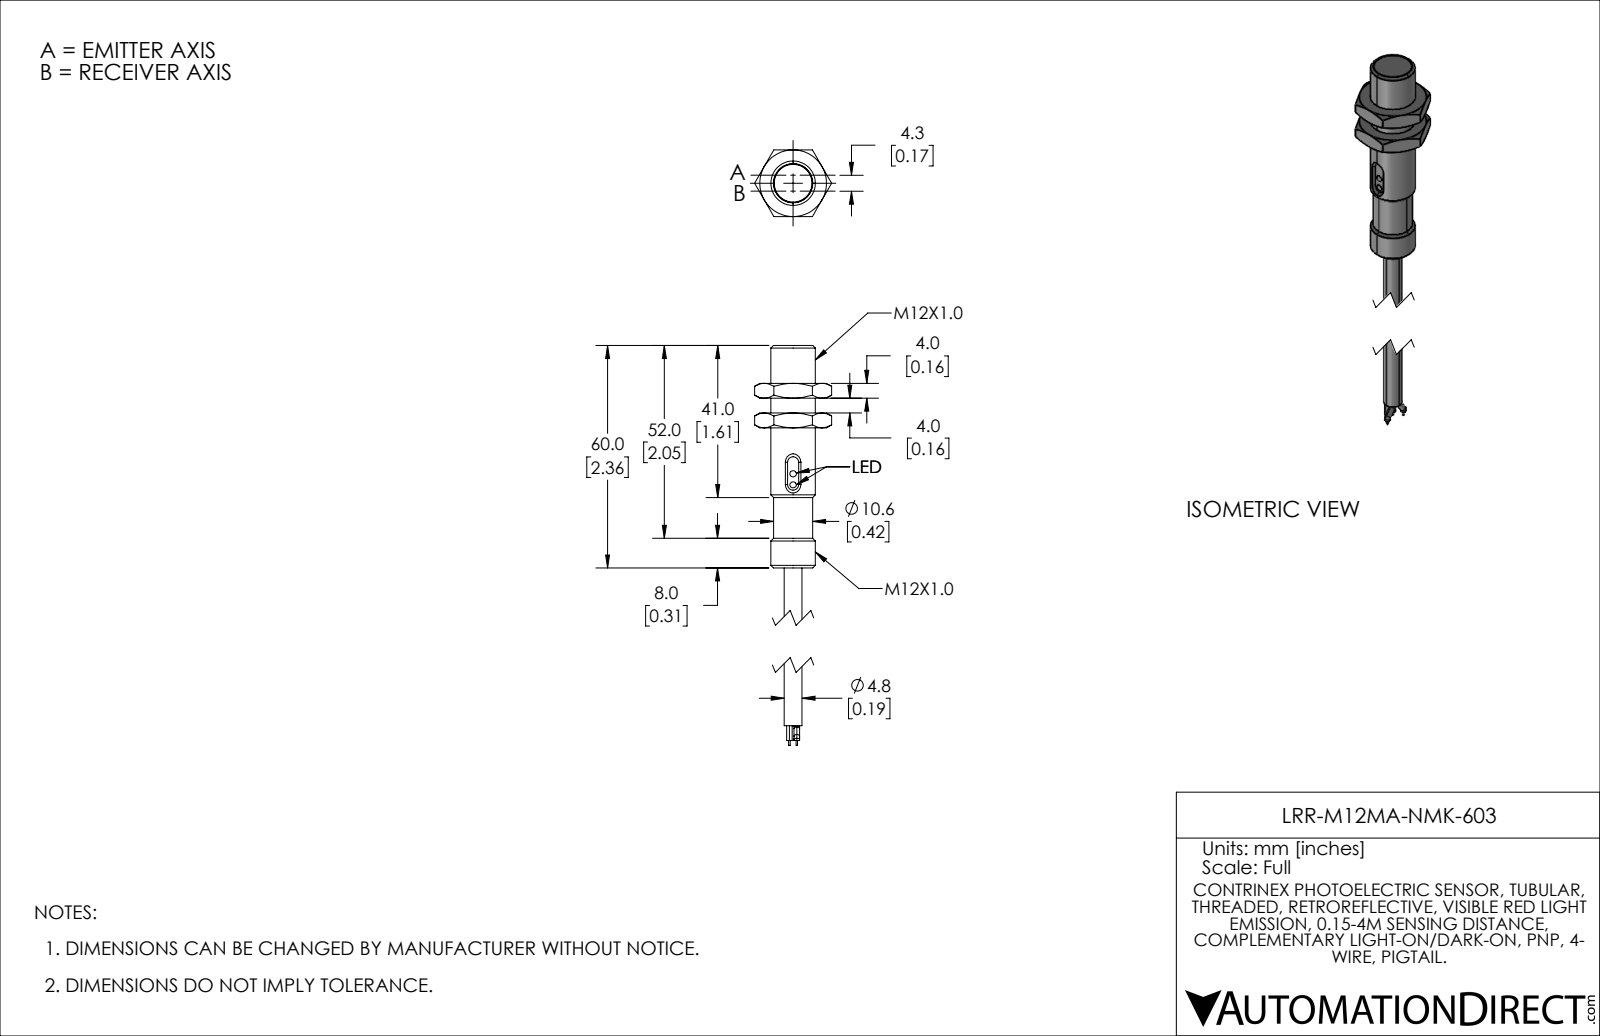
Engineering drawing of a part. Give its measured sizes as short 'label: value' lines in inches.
name: LRR-M12MA-NMK-603
written by: SolidWorks 2021 (AUTOMOTIVE_DESIGN)
unit: in
bodies: 3 solids, 141 faces (31 planar, 44 cylindrical, 66 other)
size: 5.72 × 0.818 × 0.709
volume: 0.624 in³; area: 8.604 in²
holes: 1× ⌀0.402
bosses: 6× ⌀0.059, 4× ⌀0.016, 1× ⌀0.472, 1× ⌀0.415, 1× ⌀0.189
face distances: 0.394, 0.709, 0.236, 0.63, 0.157, 0.787, 1.024, 2.354, 1.961, 1.724
